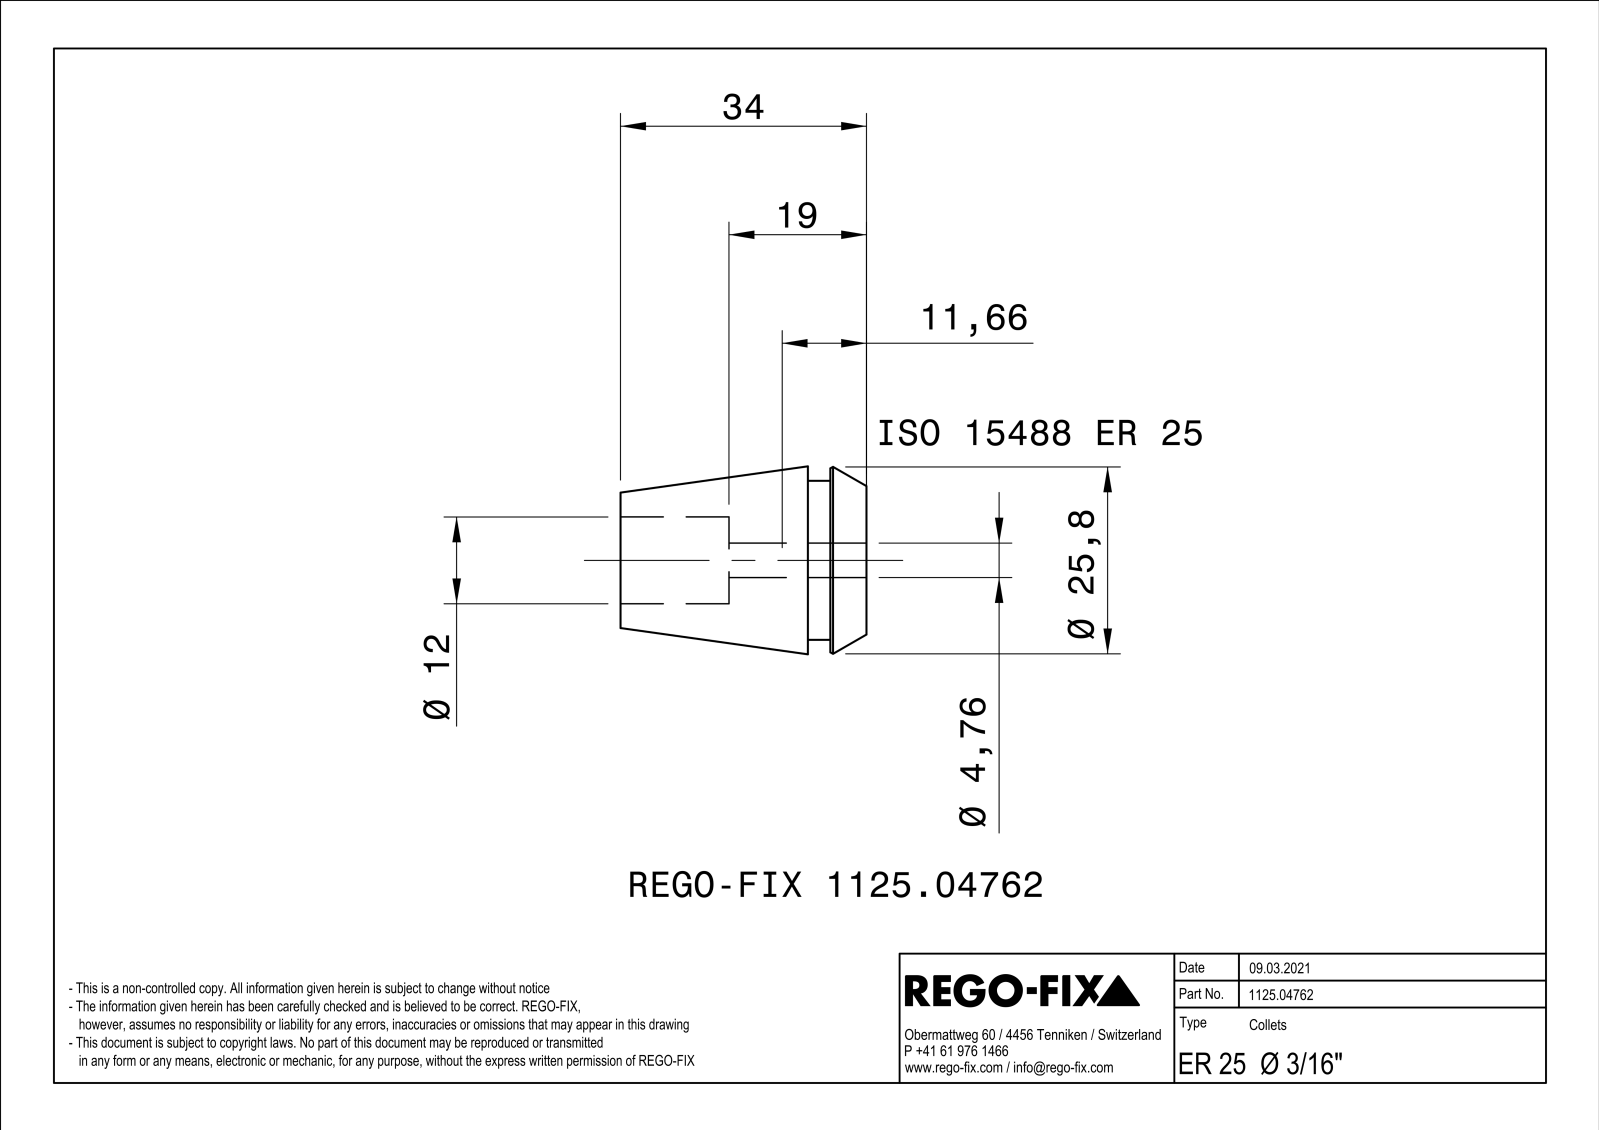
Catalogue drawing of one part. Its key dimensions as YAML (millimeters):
part_name: "NOCUT"
step_written_by: "SIEMENS PLM Software Solid Edge ST10 (AUTOMOTIVE_DESIGN)"
units: millimeters
bodies: {solids: 1, faces: 272, planar: 104, cylindrical: 48, other: 120}
overall_size: [34, 25.99, 25.99]
volume: 9846
surface_area: 9300
round_holes:
  - {diameter: 12, count: 1}
round_bosses_or_shafts:
  - {diameter: 22, count: 1}
partial_cylinders:
  - {radius: 40, count: 8}
  - {radius: 2.38, count: 1}
face_to_face_distances: [0.6, 0.62, 0.58, 8.1, 34, 25.9, 5, 3.1, 29, 19]
